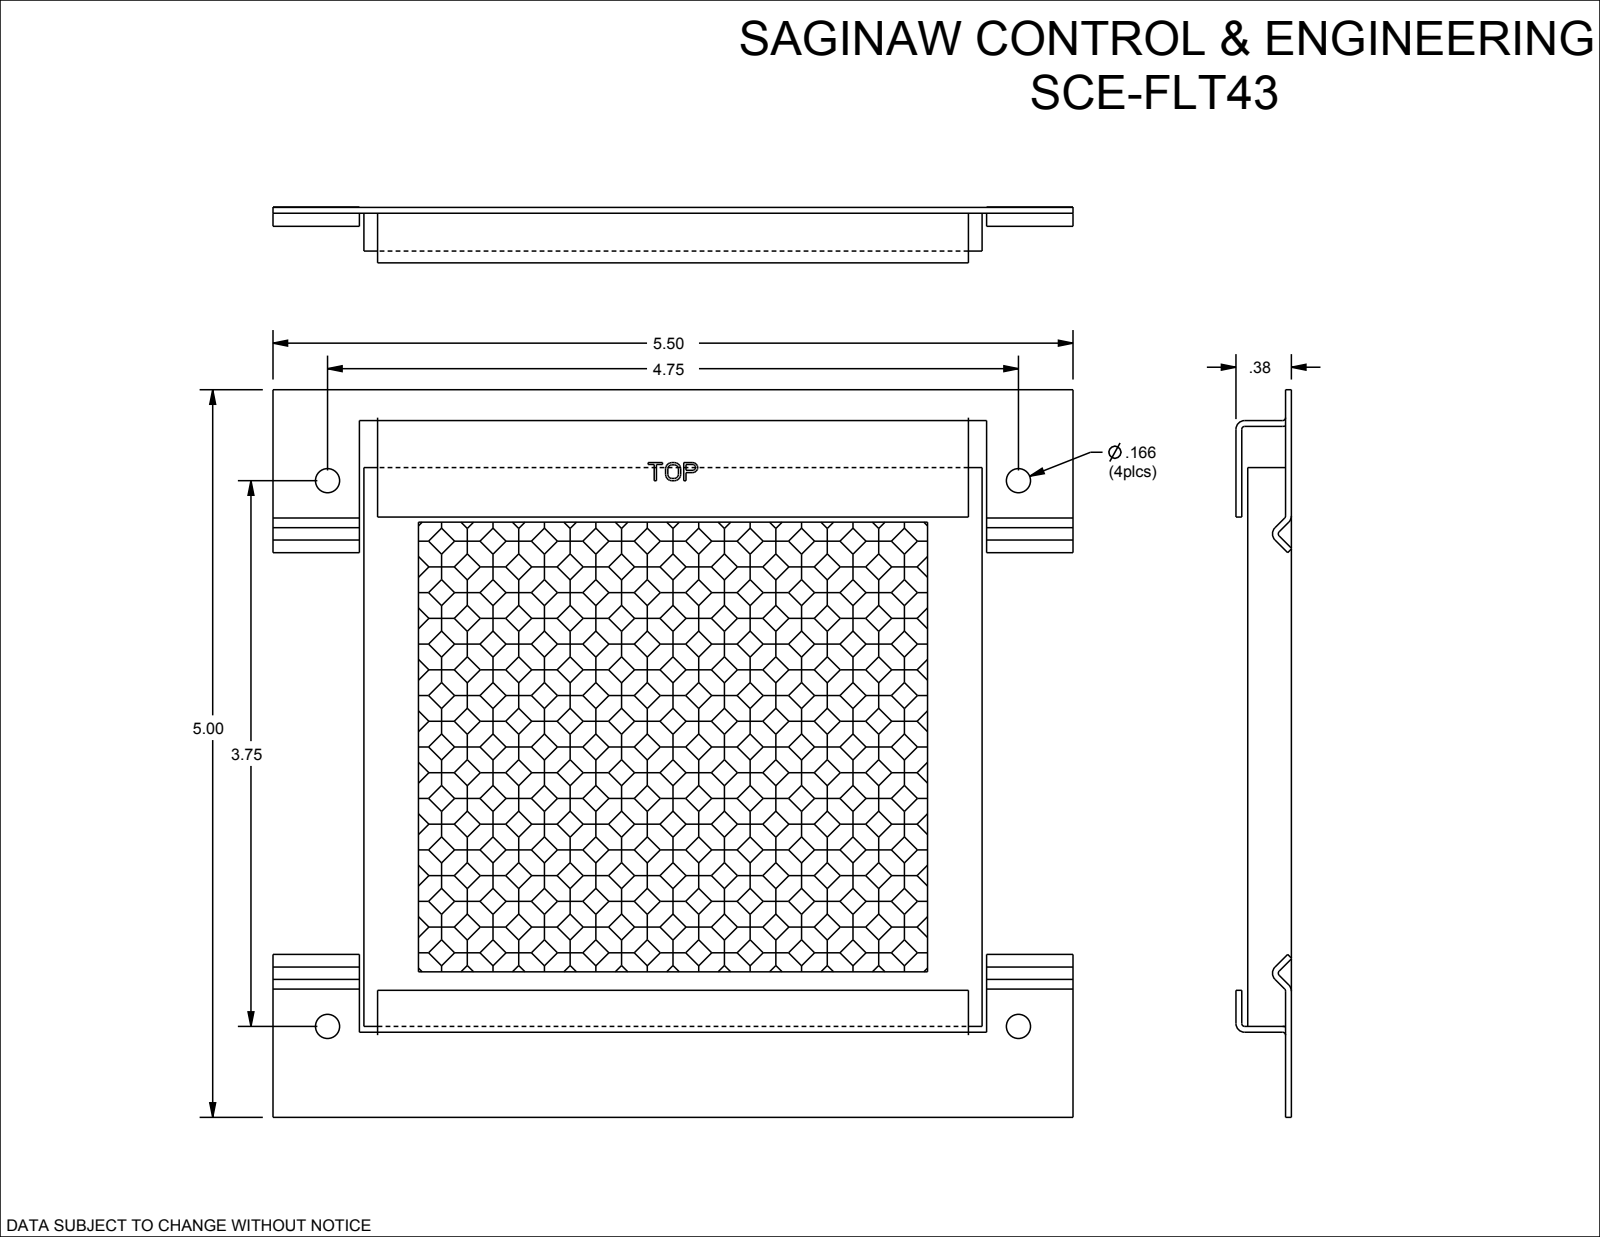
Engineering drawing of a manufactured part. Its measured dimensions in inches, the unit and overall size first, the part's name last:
Units: inches
Overall size (bounding box): 5.5 × 5 × 0.384
Round holes (diameter × count): ⌀0.166 ×4
Round bosses / shafts (diameter × count): ⌀0.125 ×31, ⌀0.125 ×7
Partial cylindrical surfaces — rounded edges, fillets, slot ends (radius × count): R0.02 ×8, R0.06 ×8
Main face-to-face distances: 0.04, 0.3, 0.26, 0.04, 0.081, 0.341, 0.381, 0.041, 0.301, 0.341
Hole centre spacings: 3.75, 4.75, 6.052
Volume: 3.048 in³ · Surface area: 72.19 in²
Bodies: 3 solids, 1218 faces (470 planar, 748 cylindrical, 0 other)
Part name (STEP PRODUCT): SCE-FLT43
STEP written by: SolidWorks 2019 (CONFIG_CONTROL_DESIGN)
